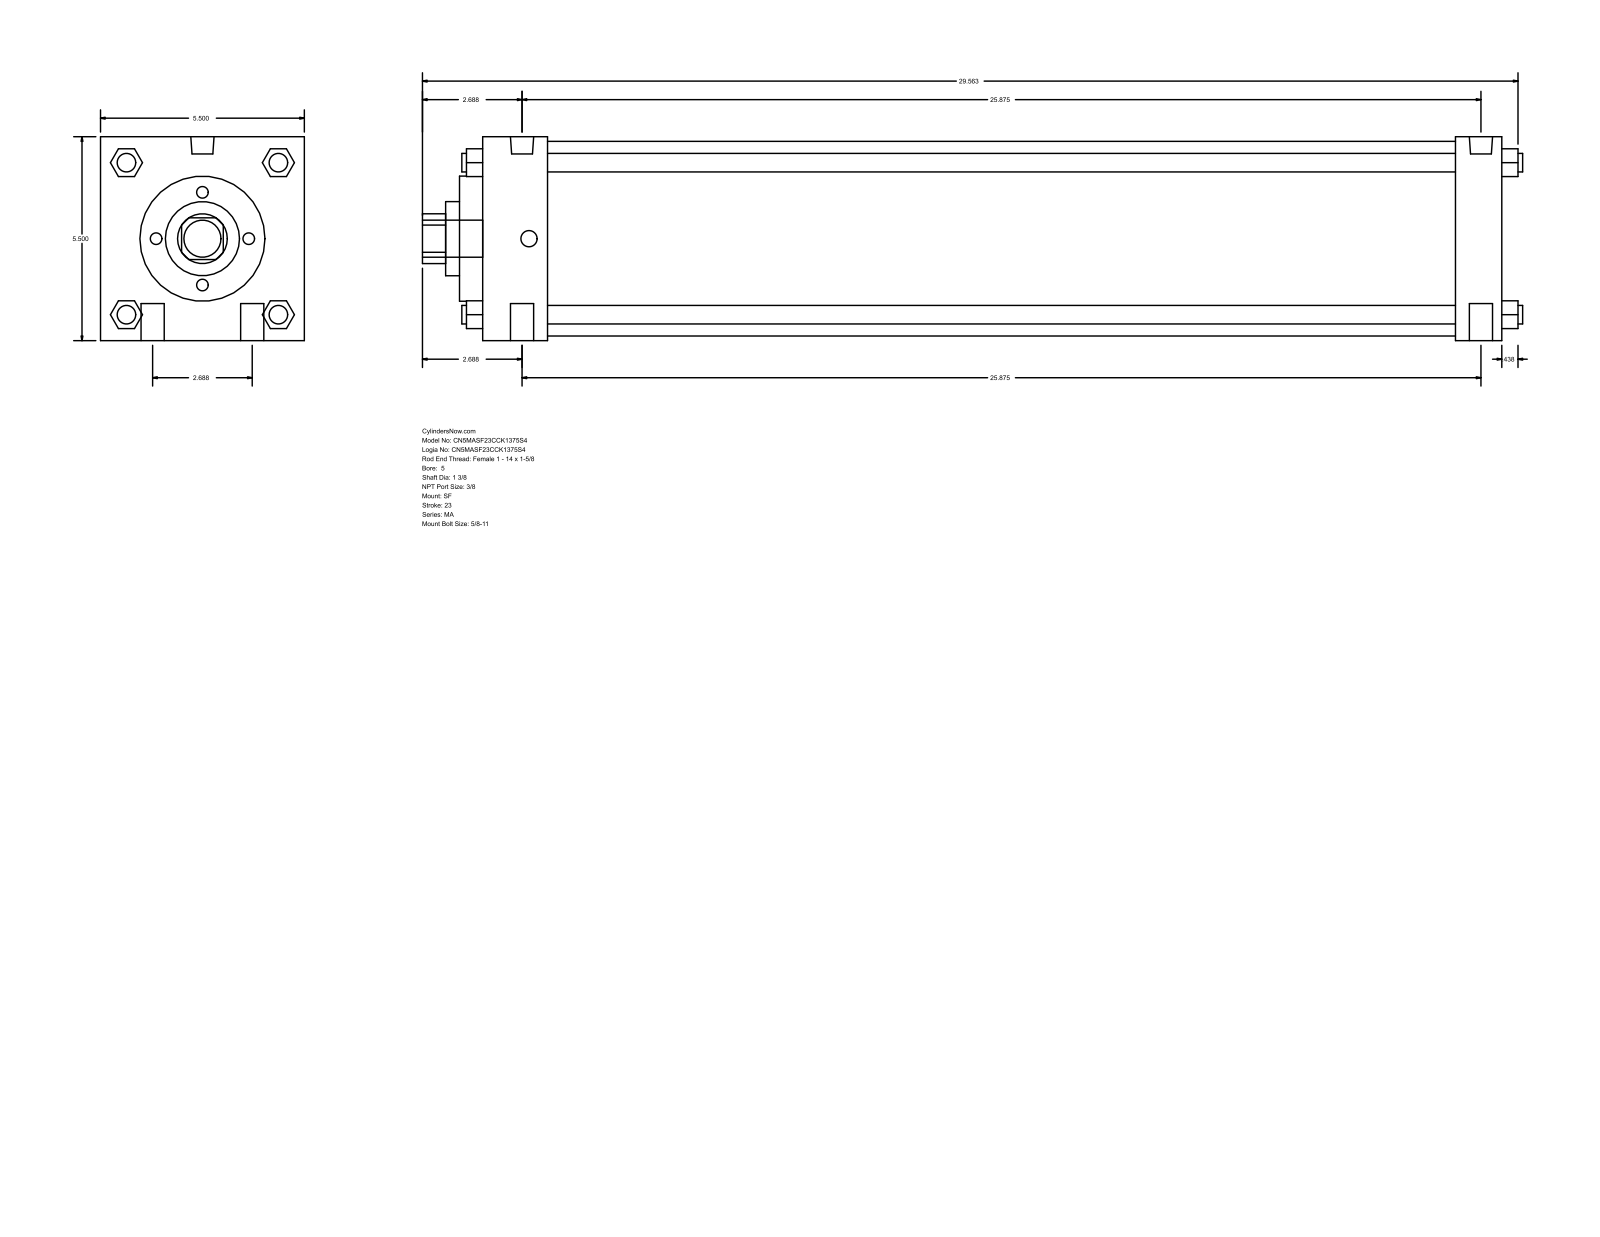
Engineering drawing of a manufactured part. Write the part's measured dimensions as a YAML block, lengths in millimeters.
part_name: "MA_SF__0500_1.375"
step_written_by: "GSSL Pune (CONFIG_CONTROL_DESIGN)"
units: millimeters
bodies: {solids: 0, faces: 126, planar: 95, cylindrical: 31, other: 0}
overall_size: [754.06, 139.7, 139.7]
round_holes:
  - {diameter: 34.92, count: 1}
  - {diameter: 50.8, count: 1}
  - {diameter: 85.72, count: 1}
  - {diameter: 133.35, count: 1}
round_bosses_or_shafts:
  - {diameter: 15.88, count: 4}
  - {diameter: 12.7, count: 4}
  - {diameter: 15.93, count: 2}
  - {diameter: 11.11, count: 2}
  - {diameter: 25.4, count: 1}
partial_cylinders:
  - {radius: 17.06, count: 1}
face_to_face_distances: [139.7, 698.5, 44.45, 666.75, 622.3, 654.05, 31.75, 15.87, 60.32, 682.62]
